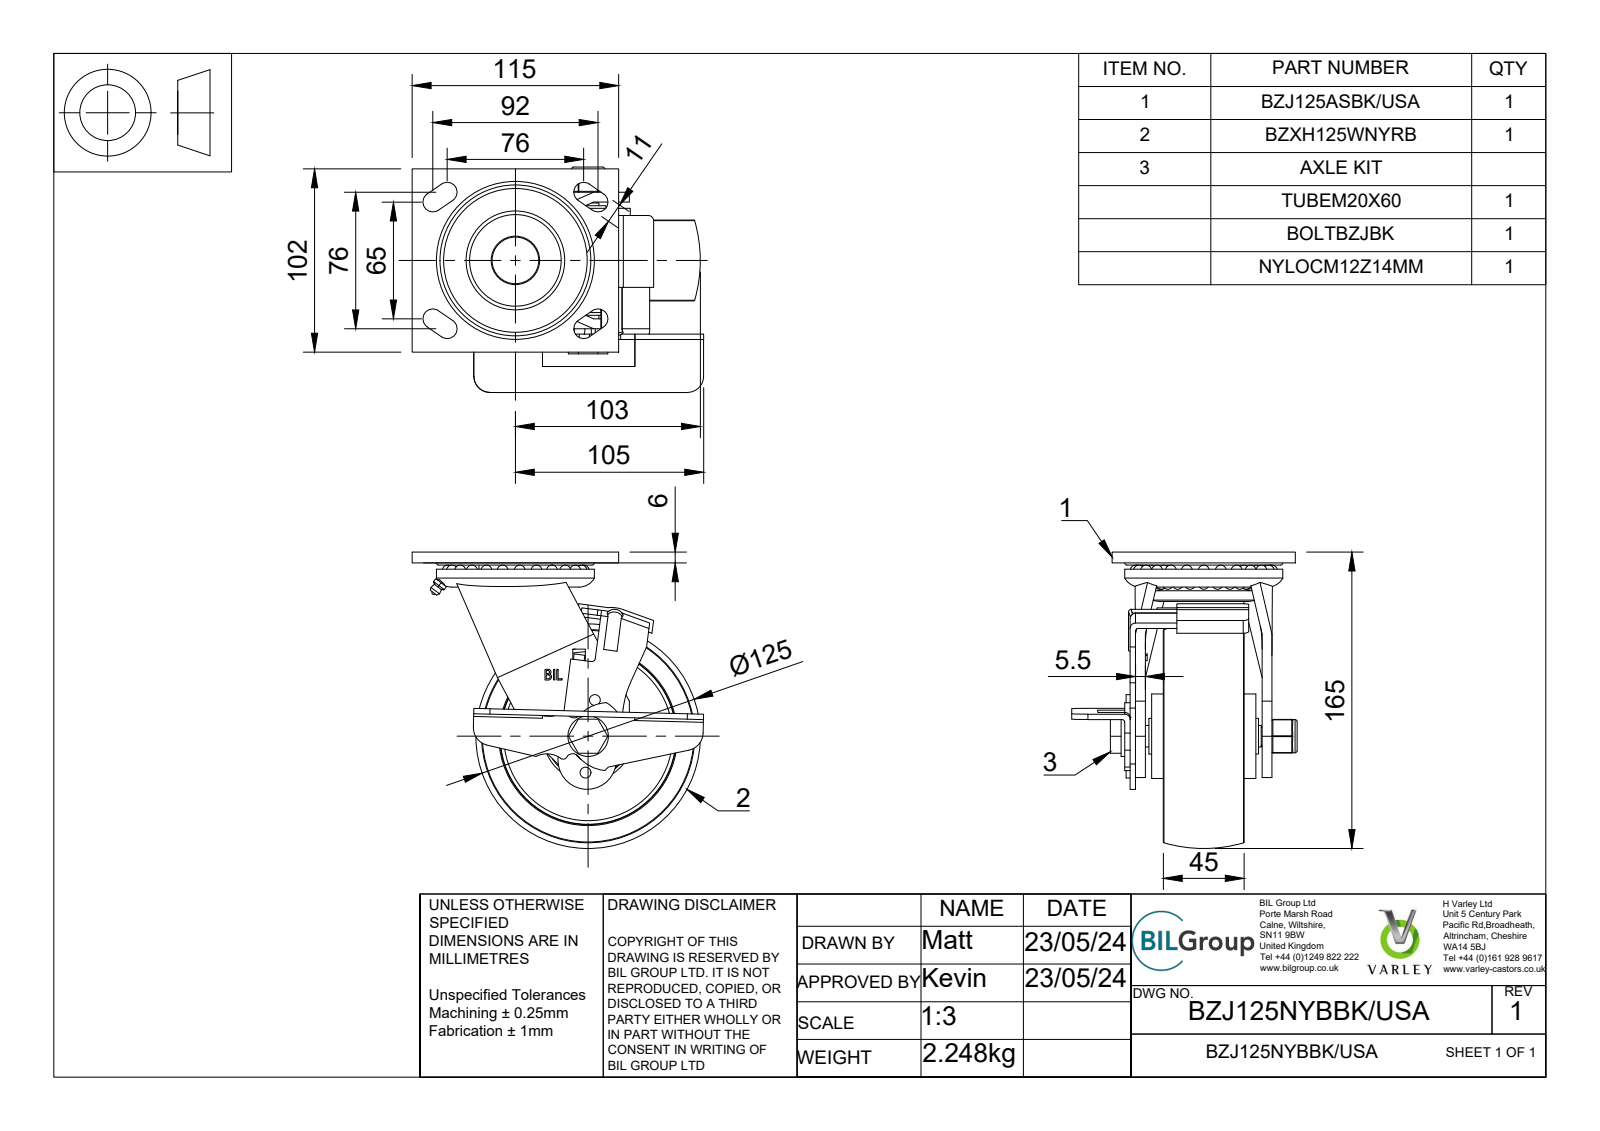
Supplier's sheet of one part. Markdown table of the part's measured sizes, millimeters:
| quantity | value |
| --- | --- |
| part name | BZJ125NYBBK/USA v3; BZJ125ASUSA v1; FABRICATED STEEL TOP PLATES; FABRICATED STEEL TOP PLATES Geometry (+6 more) |
| STEP written by | Autodesk Translation Framework v13.14.0.145 (AUTOMOTIVE_DESIGN) |
| units | millimeters |
| bodies | 66 solids, 512 faces (268 planar, 132 cylindrical, 112 other) |
| overall size | 165 × 162.33 × 125.5 |
| volume | 594 626 mm³ |
| surface area | 208 769 mm² |
| round holes (diameter × count) | 12 × 1, 12.5 × 1, 13 × 1, 14 × 1, 17 × 1, 20 × 1, 35 × 1, 40.9 × 1, 83 × 1 |
| round bosses / shafts (diameter × count) | 7.5 × 8, 6 × 2, 88 × 1, 69 × 1, 57 × 1, 47 × 1, 40.62 × 1, 34 × 1 |
| partial cylindrical surfaces (radius × count) | 0.5 × 18, 5.5 × 8, 3 × 6, 1.5 × 4, 2 × 2, 2.45 × 2, 3.96 × 2, 8.5 × 2 |
| main face-to-face distances | 3, 27.5, 10, 43, 33, 6, 5.5, 70.5, 37.5, 15.5 |
